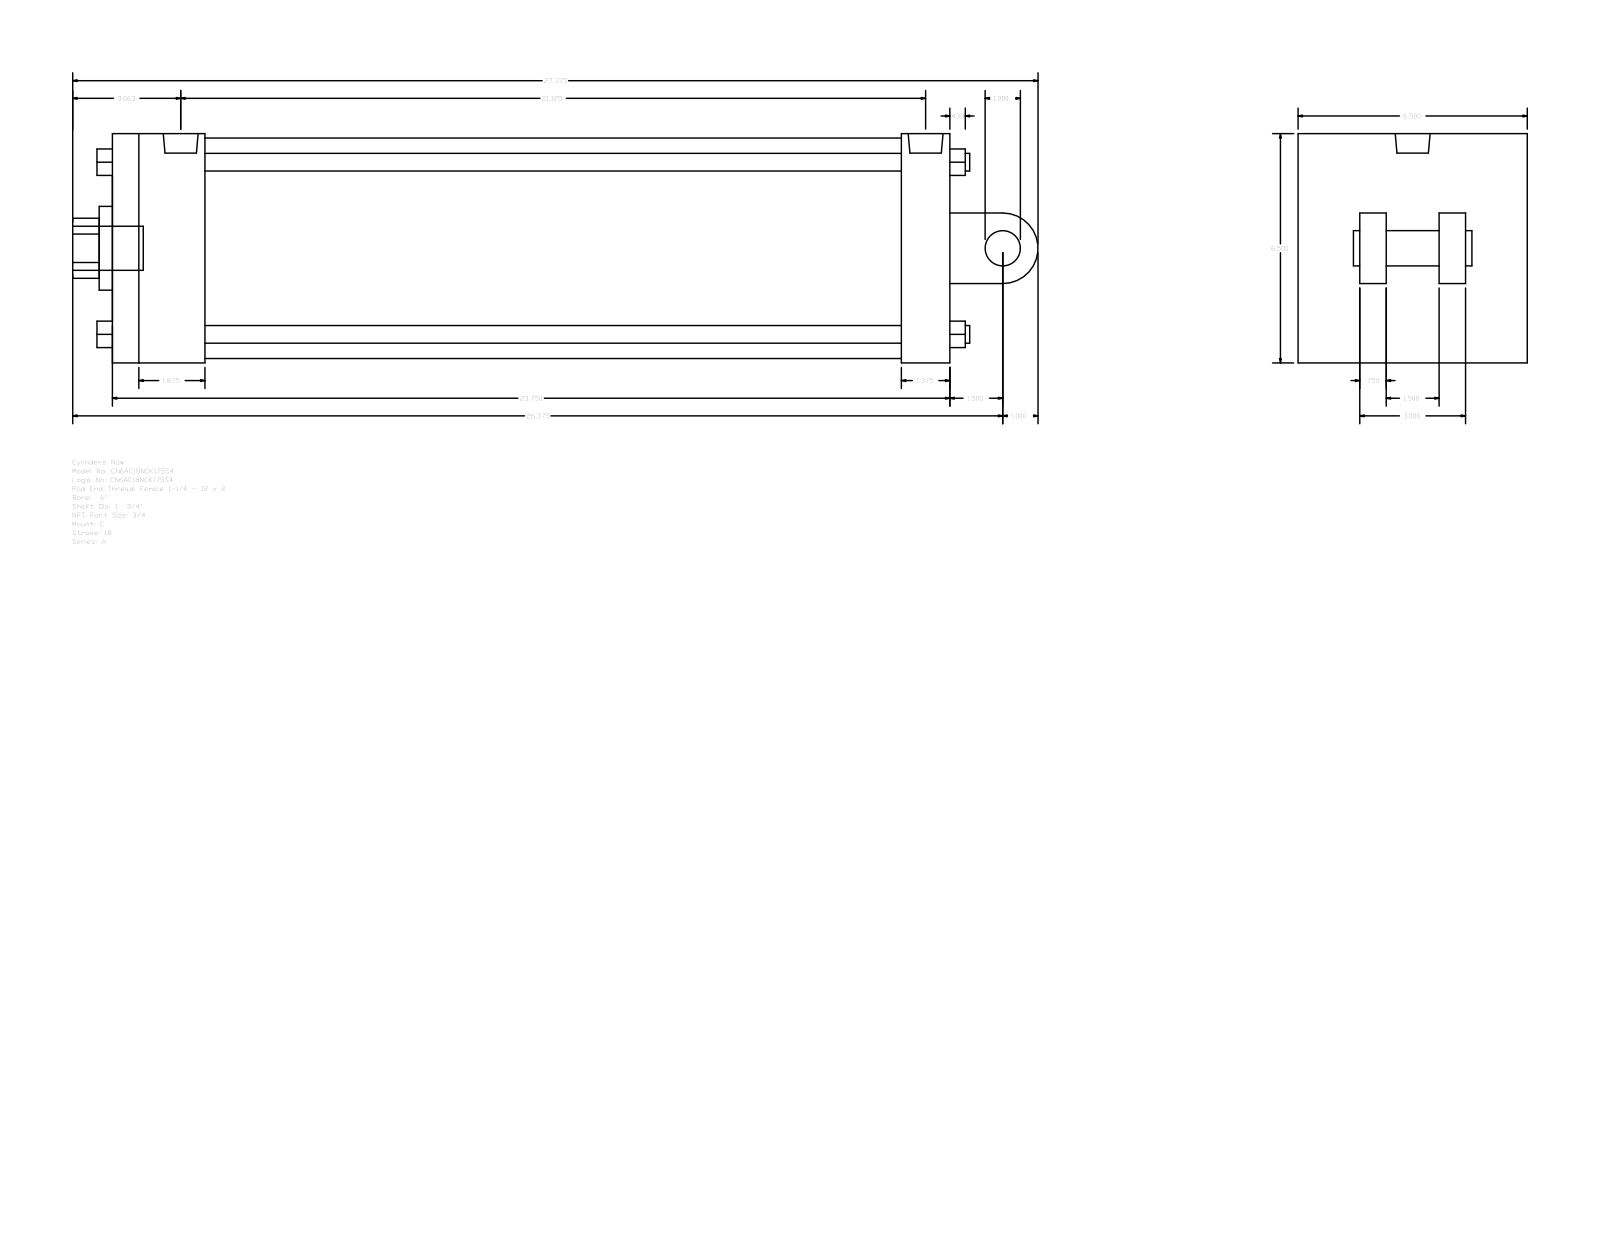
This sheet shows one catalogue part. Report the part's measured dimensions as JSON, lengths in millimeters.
{"part_name": "A_C__0600_1.75", "step_written_by": "GSSL Pune (CONFIG_CONTROL_DESIGN)", "units": "millimeters", "bodies": {"solids": 0, "faces": 135, "planar": 102, "cylindrical": 33, "other": 0}, "overall_size": [695.33, 165.1, 165.1], "round_holes": [[15.08, 2], [25.12, 1], [44.45, 1], [60.33, 1], [158.75, 1]], "round_bosses_or_shafts": [[12.7, 4], [15.08, 2], [31.75, 1], [25.4, 1], [25.12, 1]], "partial_cylinders_radius": [[21.63, 1], [25.4, 1]], "face_to_face_distances": [165.1, 603.26, 19.05, 57.15, 66.68, 536.58, 568.33, 501.65, 34.93, 44.45], "hole_center_spacings": [5.56]}
